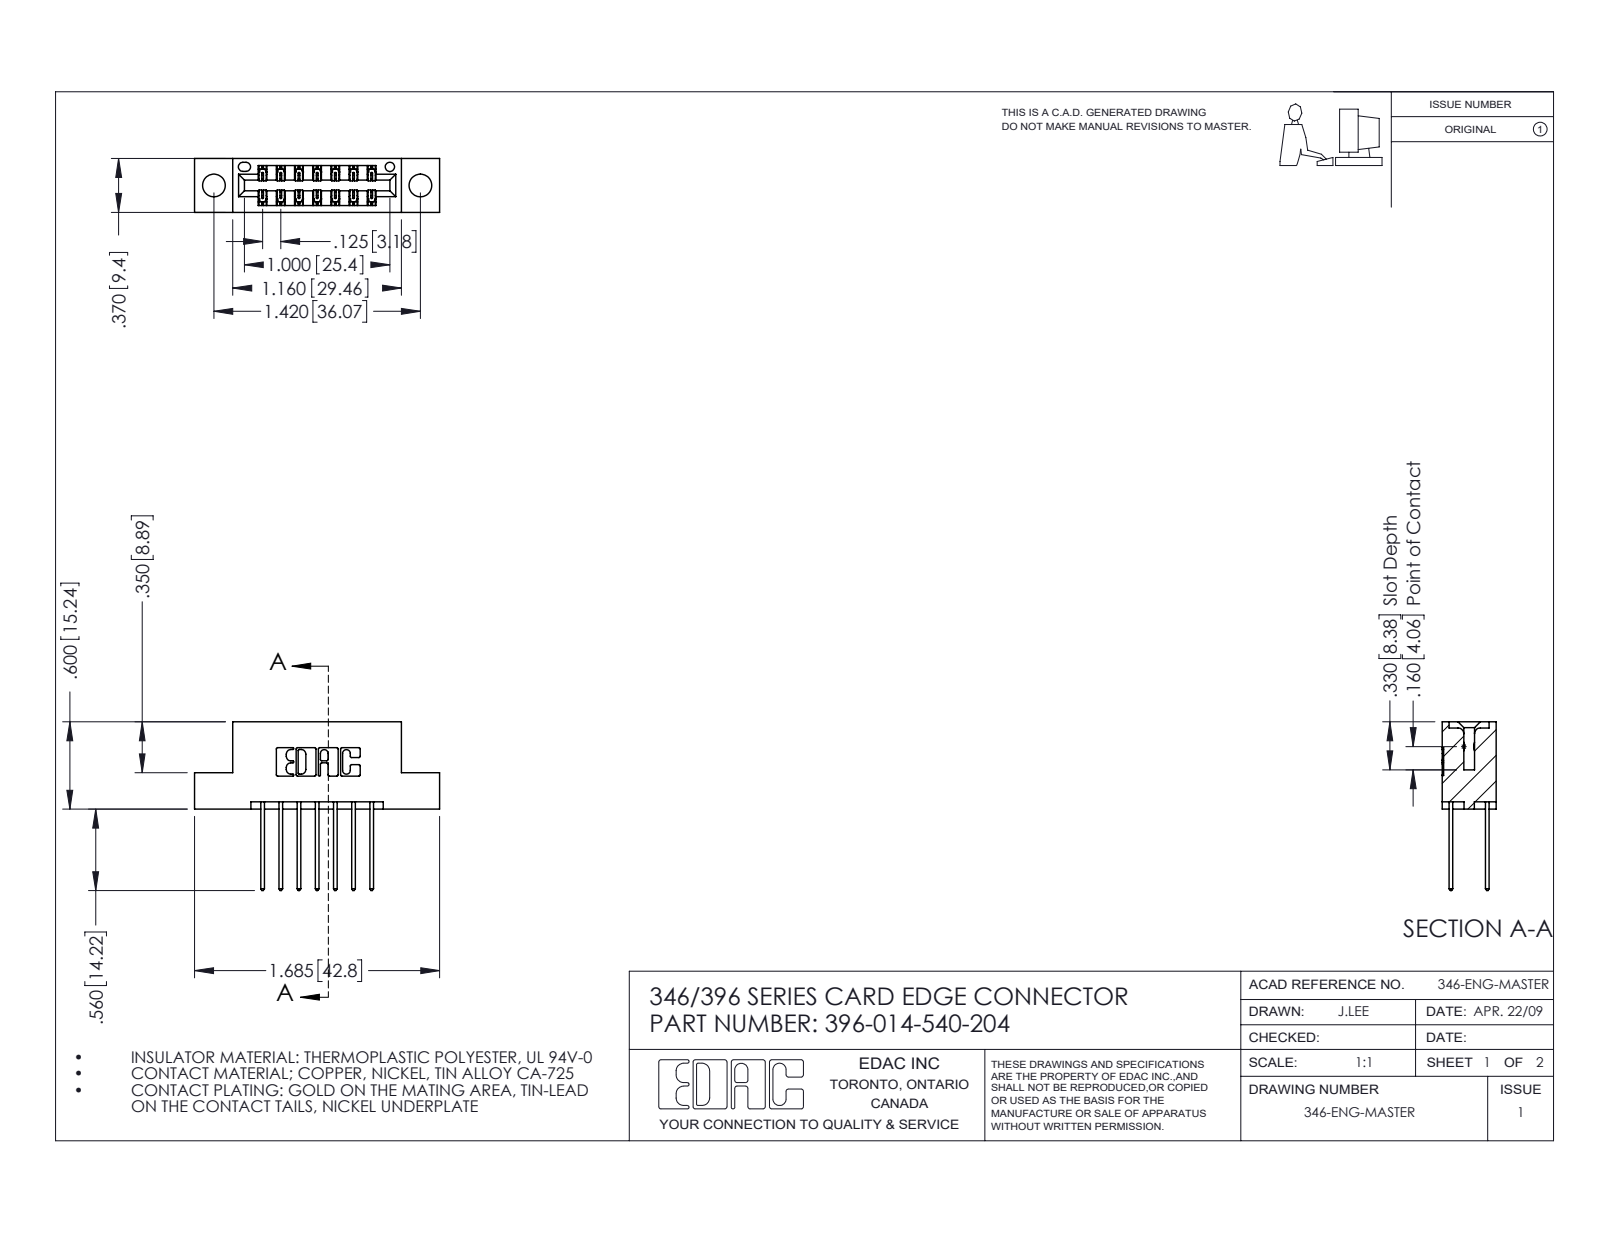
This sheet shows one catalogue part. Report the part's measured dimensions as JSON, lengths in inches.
{"part_name": "396-014-540-204; 346 Part_Flush Mounting Lugs - 0.156 Dia-TH; 345-292-001_345-293-140", "step_written_by": "SolidWorks 2016 (CONFIG_CONTROL_DESIGN)", "units": "inches", "bodies": {"solids": 15, "faces": 850, "planar": 566, "cylindrical": 284, "other": 0}, "overall_size": [1.685, 1.16, 0.37], "volume_in3": 0.236, "surface_area_in2": 7.486, "round_holes": [[0.156, 2], [0.064, 1]], "partial_cylinders_radius": [[0.01, 22], [0.006, 21], [0.01, 14], [0.007, 6], [0.031, 6], [0.026, 3], [0.014, 2], [0.022, 2]], "face_to_face_distances": [0.25, 0.048, 0.322, 0.37, 0.025, 0.072, 0.298, 0.275, 0.148, 0.222], "hole_center_spacings": [0.246, 1.217, 1.42]}
